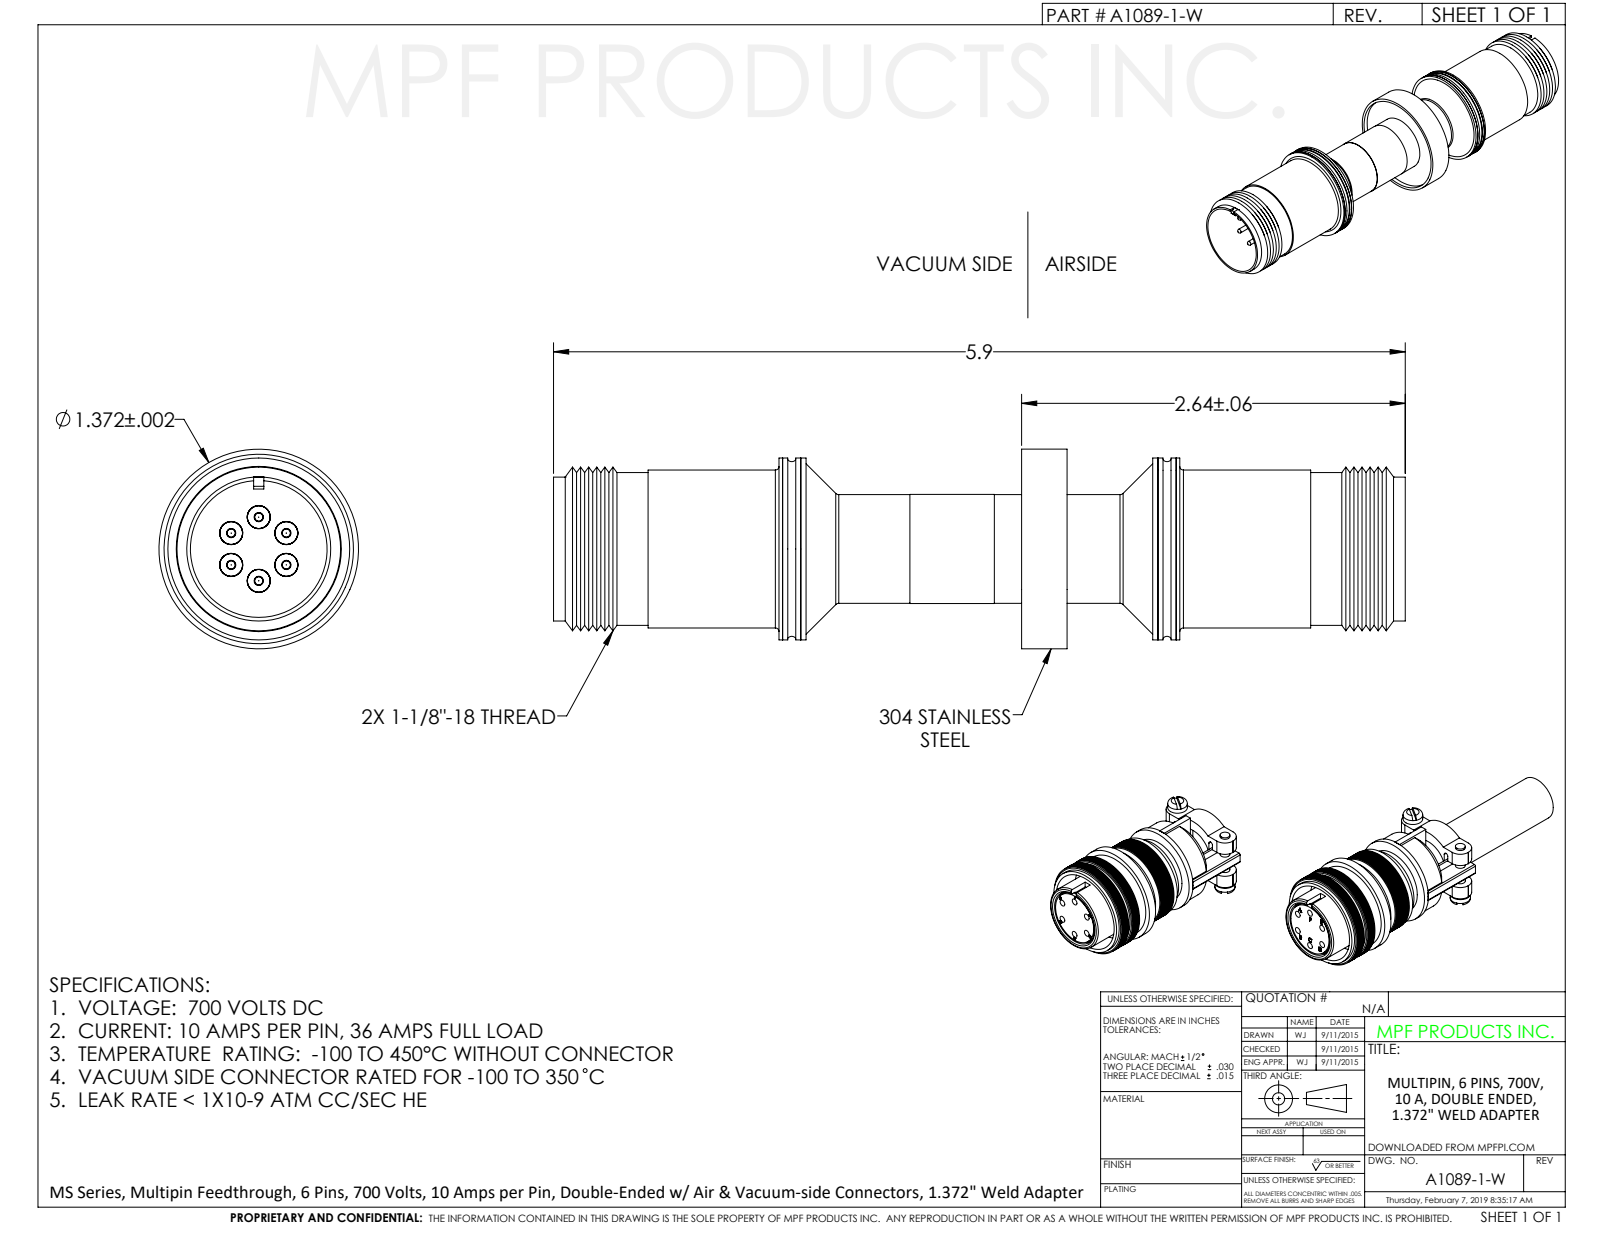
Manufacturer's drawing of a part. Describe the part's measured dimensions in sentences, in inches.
The part is named "A1089-1-W". Its 3-D file was written by "SolidWorks 2012 (CONFIG_CONTROL_DESIGN)". It is 1 solid with 455 faces: 104 planar, 222 cylindrical and 129 other. Overall it measures 5.855 by 1.372 by 1.372 inches. Its volume is 1.586 cubic inches and its surface area 60.56 square inches. Round holes: 6 of diameter 0.159, 1 of diameter 0.625, 1 of diameter 0.675, 1 of diameter 0.682, 1 of diameter 0.751, 1 of diameter 0.94, 1 of diameter 0.96, 1 of diameter 0.97, 1 of diameter 1.035, 1 of diameter 1.302. Round bosses or shafts: 6 of diameter 0.187, 6 of diameter 0.172, 6 of diameter 0.056, 5 of diameter 0.175, 1 of diameter 1.372, 1 of diameter 1.25, 1 of diameter 1.085, 1 of diameter 1.05. The main face-to-face distances are 0.05, 3.515, 0.252, 1.432, 1.18, 2.133, 2.385, 3.565, 0.04, 1.117. The hole center spacings are 0.219, 0.379, 0.38, 0.438, 0.438.
